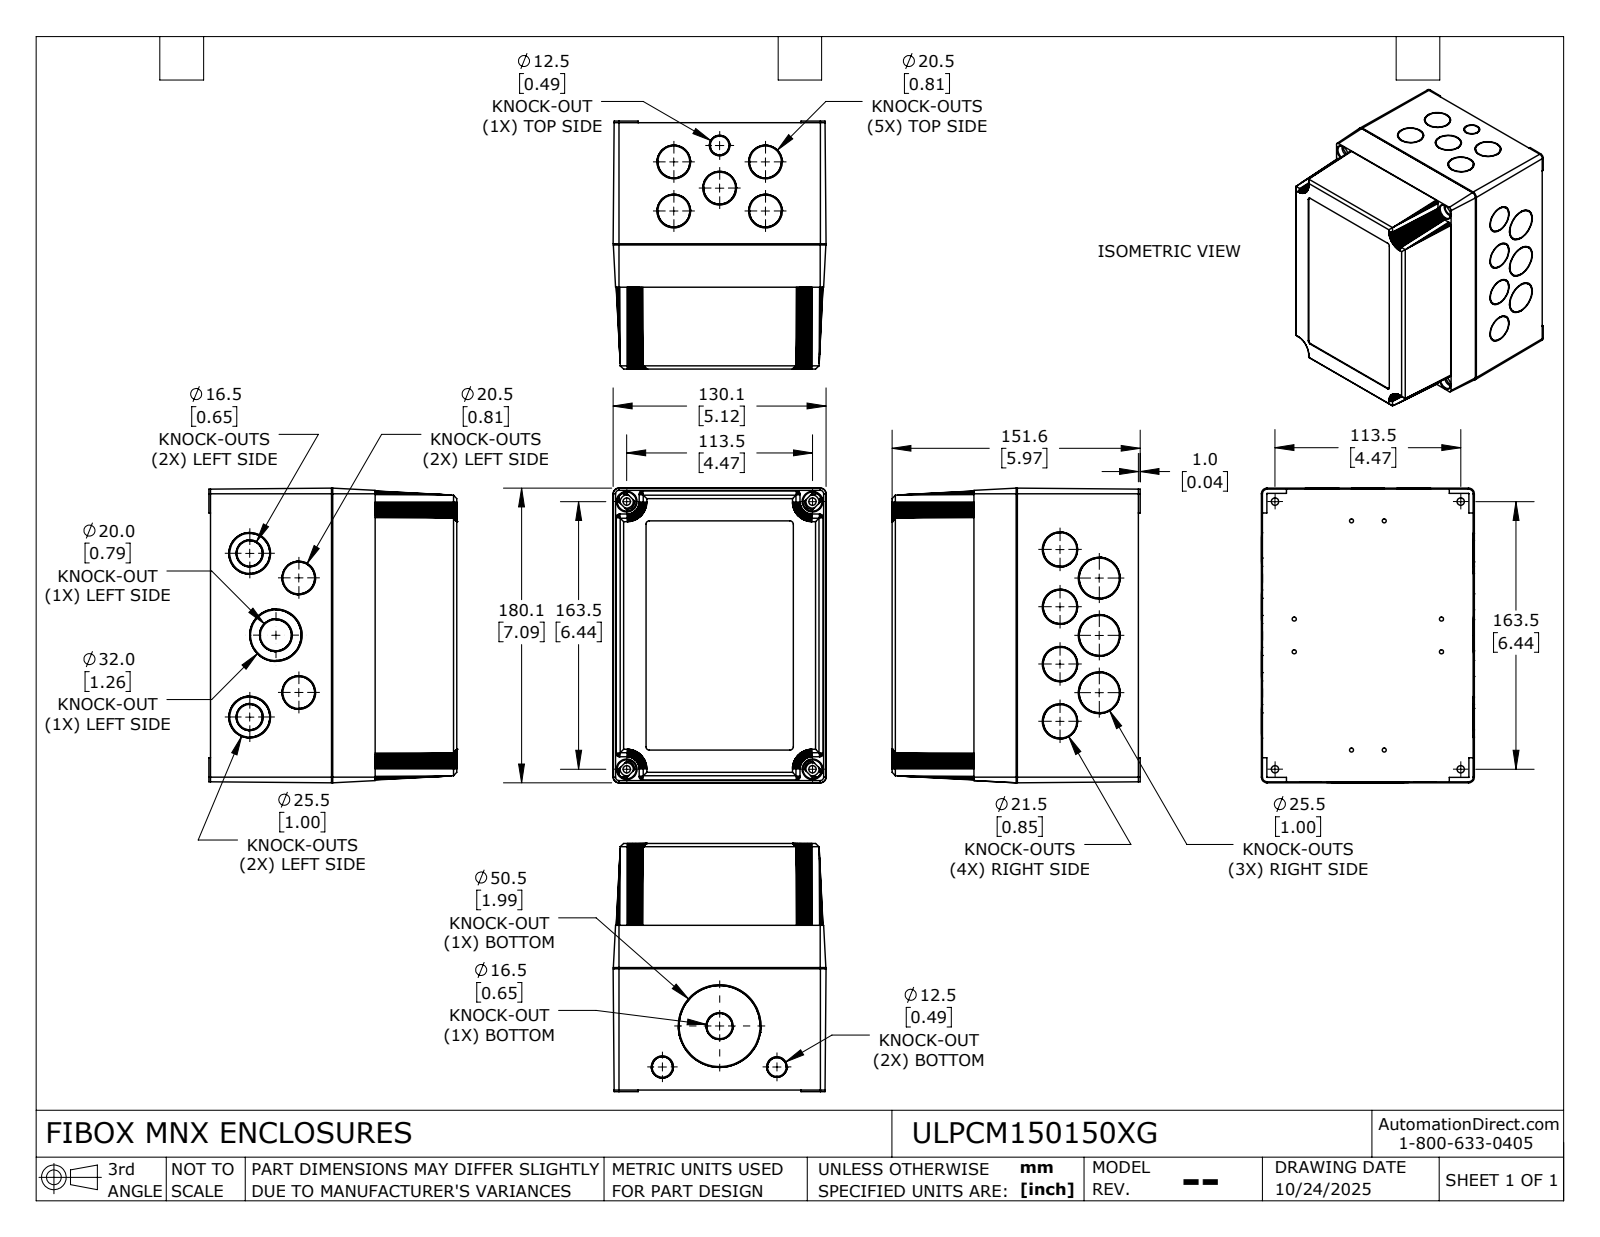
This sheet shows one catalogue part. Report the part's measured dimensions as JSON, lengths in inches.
{"part_name": "ULPCM150150XG", "step_written_by": "SolidWorks 2024 (AUTOMOTIVE_DESIGN)", "units": "inches", "bodies": {"solids": 2, "faces": 1187, "planar": 991, "cylindrical": 160, "other": 36}, "overall_size": [7.09, 5.969, 5.122], "volume_in3": 34.93, "surface_area_in2": 425.8, "round_holes": [[0.098, 8], [0.126, 8], [0.807, 7], [1.004, 5], [0.177, 4], [0.315, 4], [0.456, 4], [0.846, 4], [0.65, 3], [0.492, 1], [0.531, 1], [0.787, 1]], "round_bosses_or_shafts": [[0.315, 8], [0.768, 7], [0.965, 5], [0.807, 4], [0.61, 3], [0.453, 2], [1.949, 1], [1.22, 1]], "partial_cylinders_radius": [[0.051, 8], [0.008, 4], [0.079, 4], [0.083, 4], [0.108, 4], [0.112, 4], [0.191, 4], [0.217, 4]], "face_to_face_distances": [0.166, 0.165, 5.646, 5.811, 0.015, 0.098, 5.744, 5.909, 4.6, 0.02], "hole_center_spacings": [0.394, 1.169, 1.378, 2.756, 3.543, 0.787, 1.333, 1.575]}
